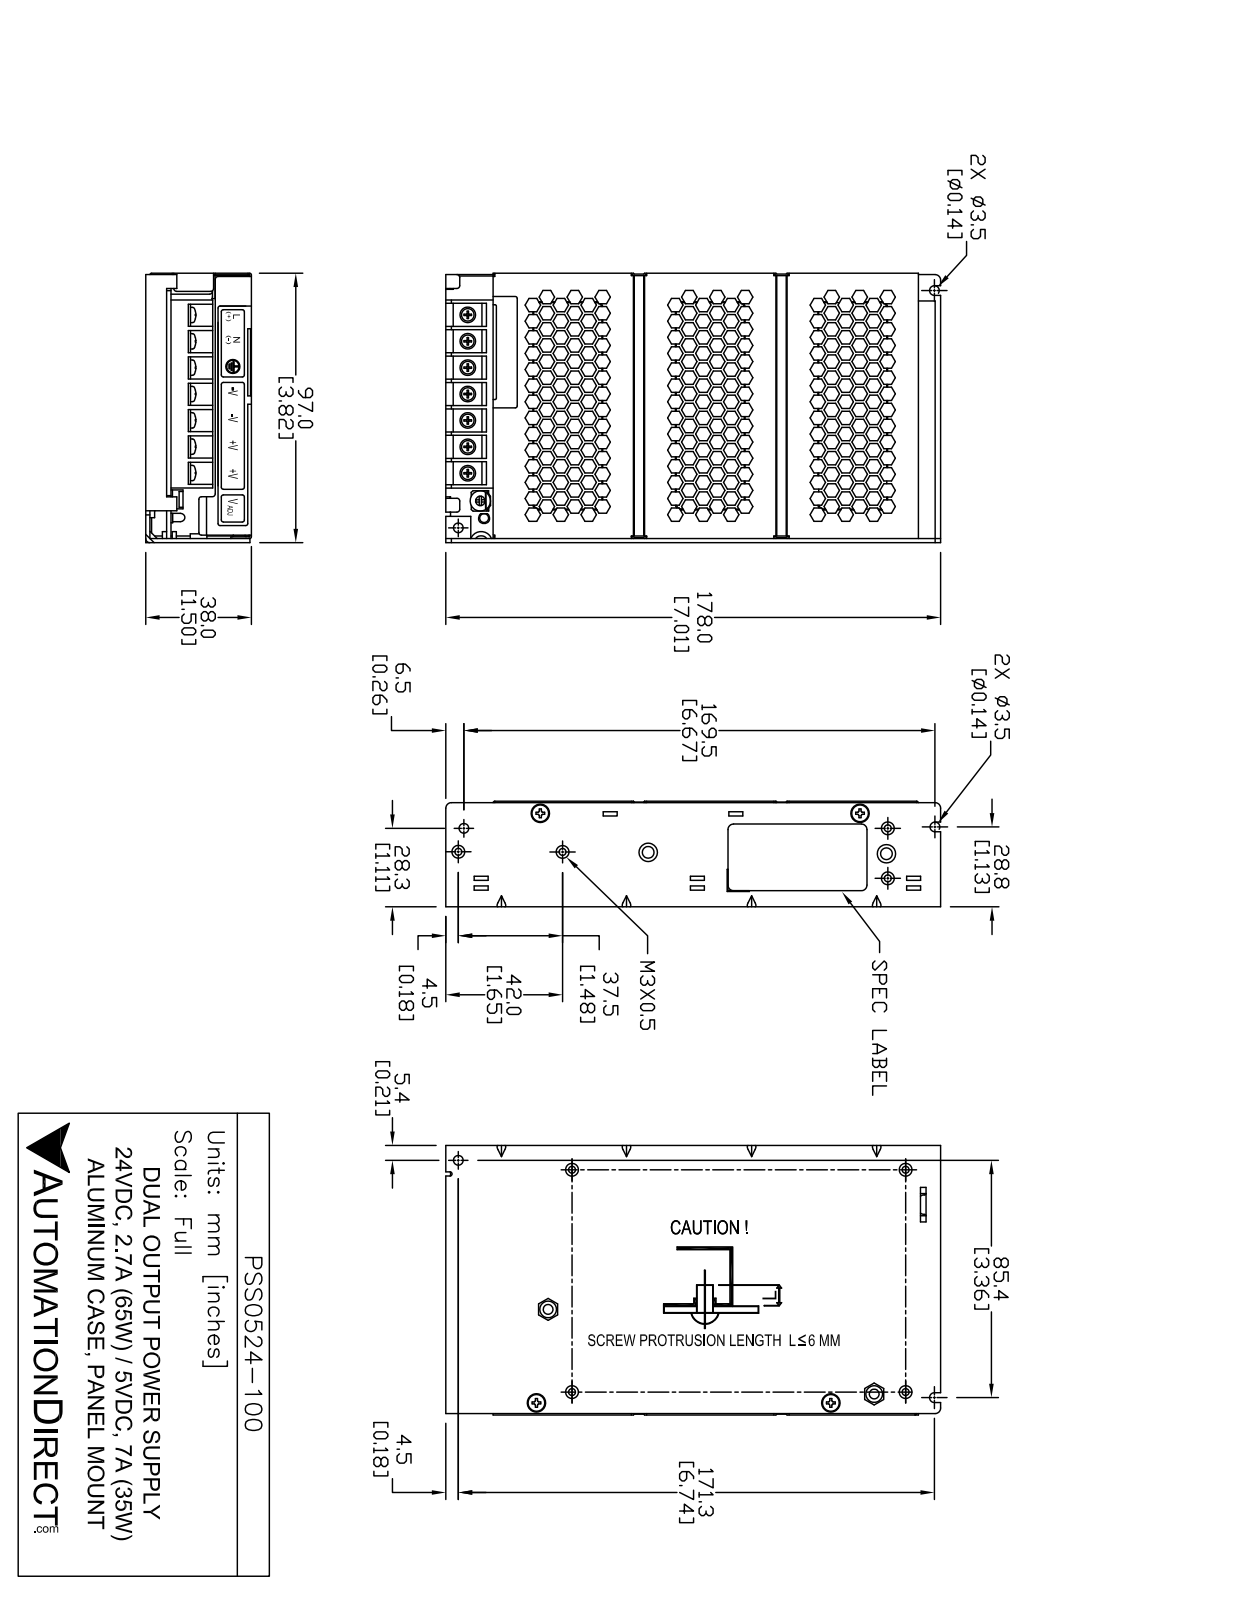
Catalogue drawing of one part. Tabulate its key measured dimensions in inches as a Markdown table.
| quantity | value |
| --- | --- |
| part name | PSS0524-100 |
| STEP written by | SolidWorks 2018 (AUTOMOTIVE_DESIGN) |
| units | inches |
| bodies | 23 solids, 3496 faces (3053 planar, 215 cylindrical, 228 other) |
| overall size | 7.008 × 3.821 × 1.496 |
| volume | 5.251 in³ |
| surface area | 224.7 in² |
| round holes (diameter × count) | 0.118 × 20, 0.067 × 7, 0.138 × 3, 0.142 × 2 |
| round bosses / shafts (diameter × count) | 0.236 × 13, 0.157 × 8, 0.268 × 7, 0.197 × 7, 0.276 × 2, 0.22 × 2, 0.209 × 2, 0.122 × 2 |
| partial cylindrical surfaces (radius × count) | 0.02 × 39, 0.008 × 28, 0.079 × 13, 0.024 × 10, 0.039 × 4, 0.197 × 4, 0.028 × 2, 0.059 × 2 |
| main face-to-face distances | 0.059, 0.024, 0.236, 0.299, 0.358, 0.295, 0.063, 1.413, 1.114, 1.437 |
| hole center spacings | 0.217, 0.374, 0.373, 0.748, 1.122, 0.746, 1.496, 6.369 |
